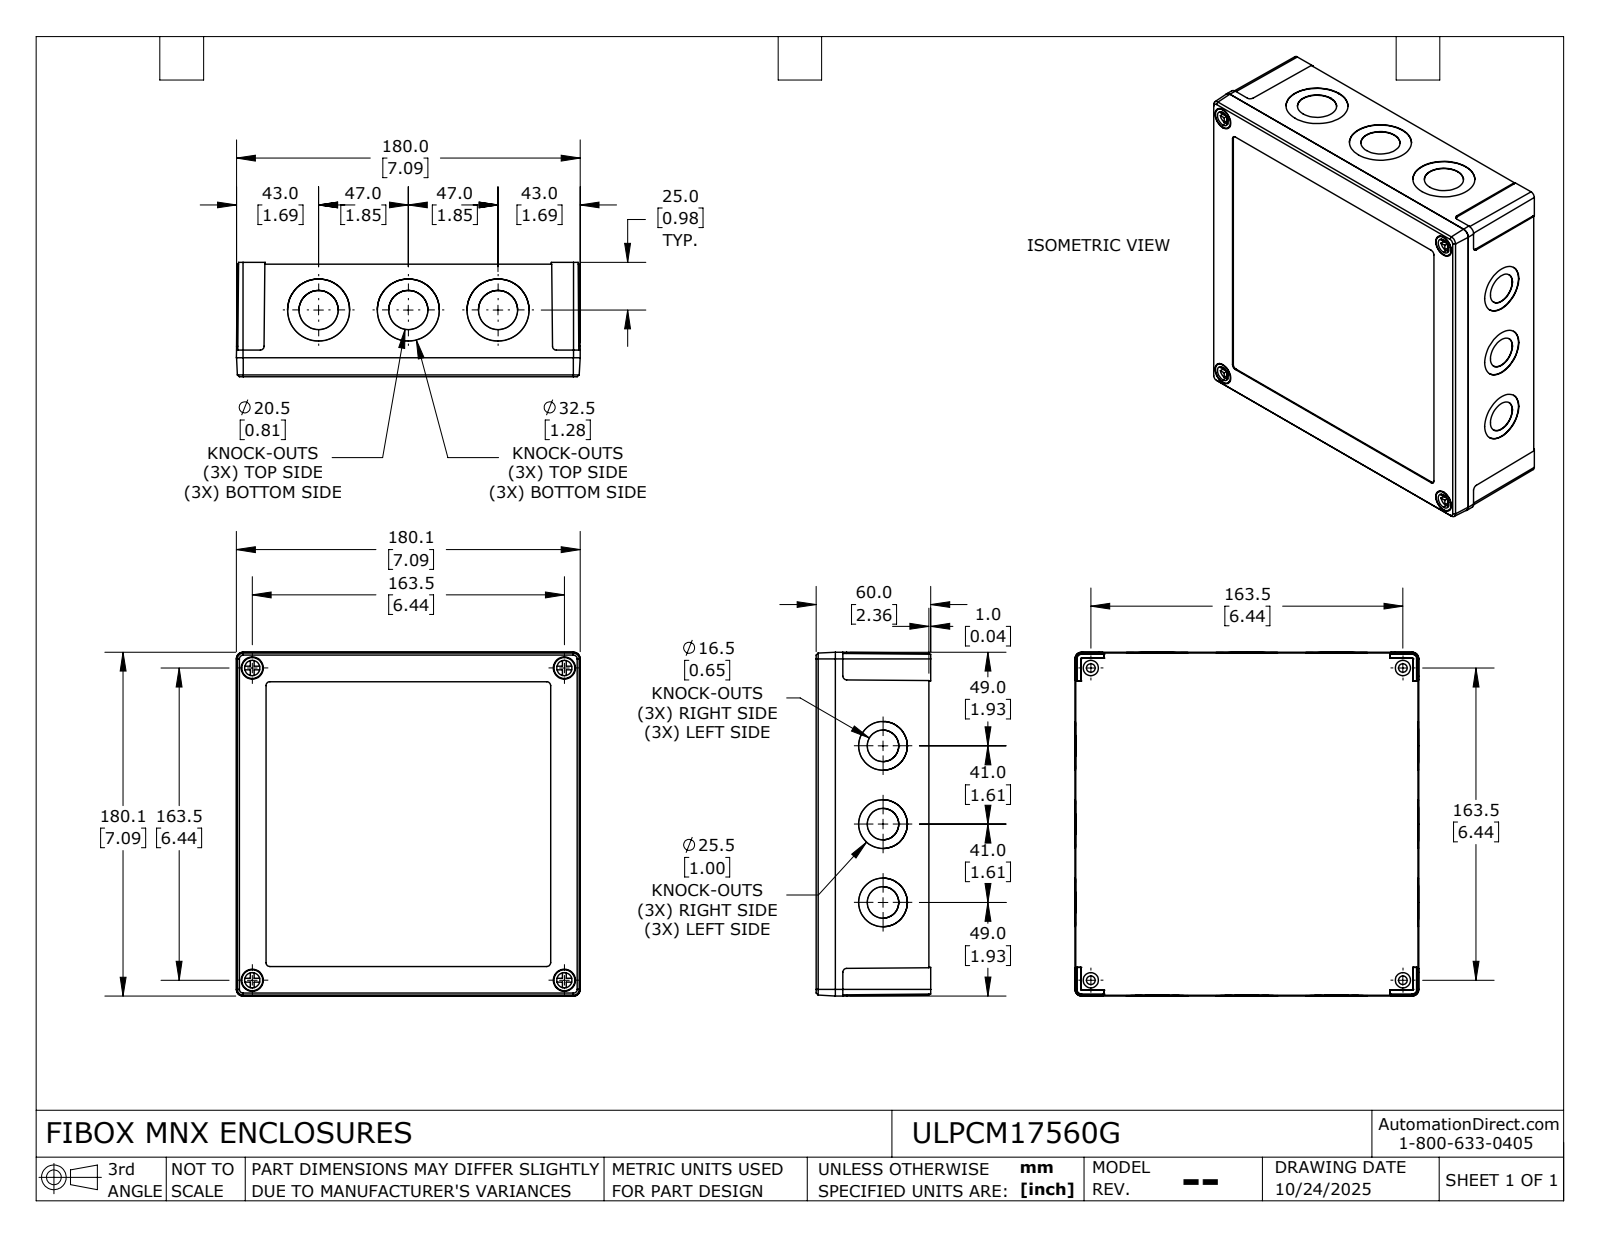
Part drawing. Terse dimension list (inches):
name: ULPCM17560G_Default
written by: SolidWorks 2024 (CONFIG_CONTROL_DESIGN)
unit: in
bodies: 6 solids, 582 faces (318 planar, 224 cylindrical, 40 other)
size: 7.091 × 7.091 × 2.362
volume: 21.68 in³; area: 342.9 in²
holes: 12× ⌀0.126, 12× ⌀0.157, 6× ⌀0.65, 6× ⌀0.807, 6× ⌀1.004, 6× ⌀1.28, 4× ⌀0.177, 4× ⌀0.315, 4× ⌀0.457
bosses: 12× ⌀0.315, 8× ⌀0.098, 4× ⌀0.433, 4× ⌀0.283
rounds: 8× R0.079, 6× R0.112, 4× R0.042, 4× R0.197, 2× R0.046
face distances: 2.205, 0.118, 2.087, 0.098, 2.303, 2.185, 0.165, 2.323, 0.02, 0.276
hole spacings: 1.333, 1.969, 2.866, 3.252, 4.79, 5.207, 5.469, 5.853
